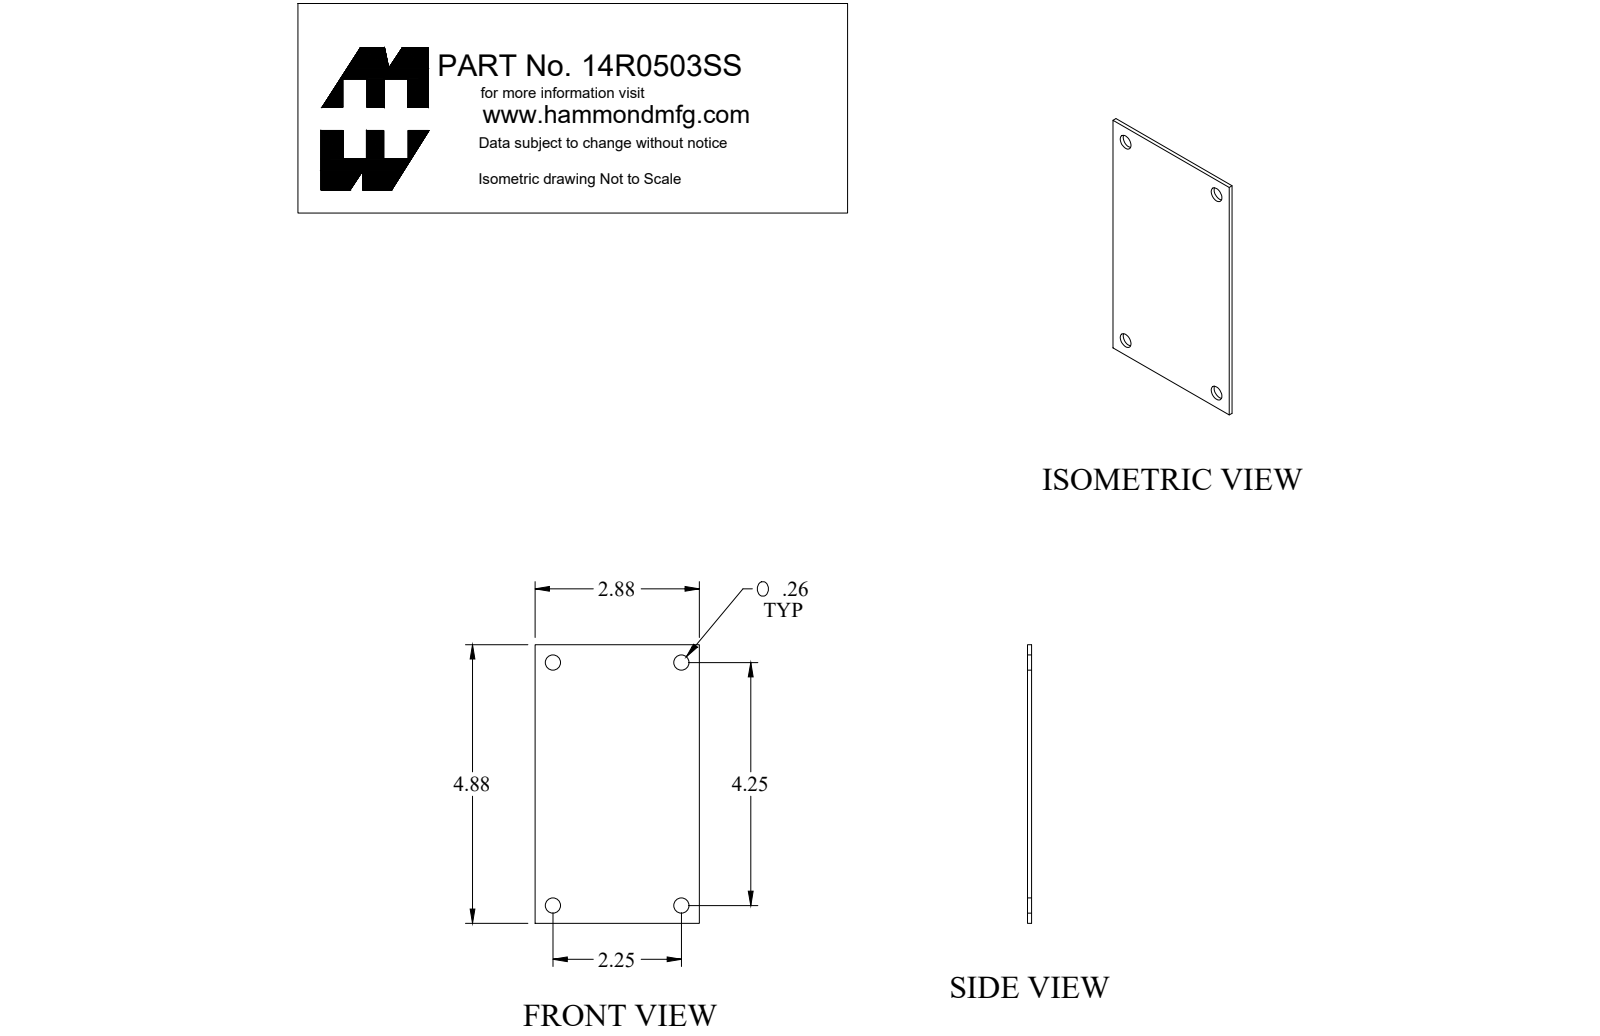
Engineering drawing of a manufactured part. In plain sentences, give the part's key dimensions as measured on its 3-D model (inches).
The part is named "14R0503SS". Its 3-D file was written by "SolidWorks 2018 (AUTOMOTIVE_DESIGN)". It is 1 solid with 10 faces: 6 planar, 4 cylindrical and 0 other. Overall it measures 4.875 by 2.875 by 0.072 inches. Its volume is 0.993 cubic inches and its surface area 28.95 square inches. Round holes: 4 of diameter 0.265. The main face-to-face distances are 0.072, 2.875, 4.875. The hole center spacings are 2.25, 4.25, 4.808.
